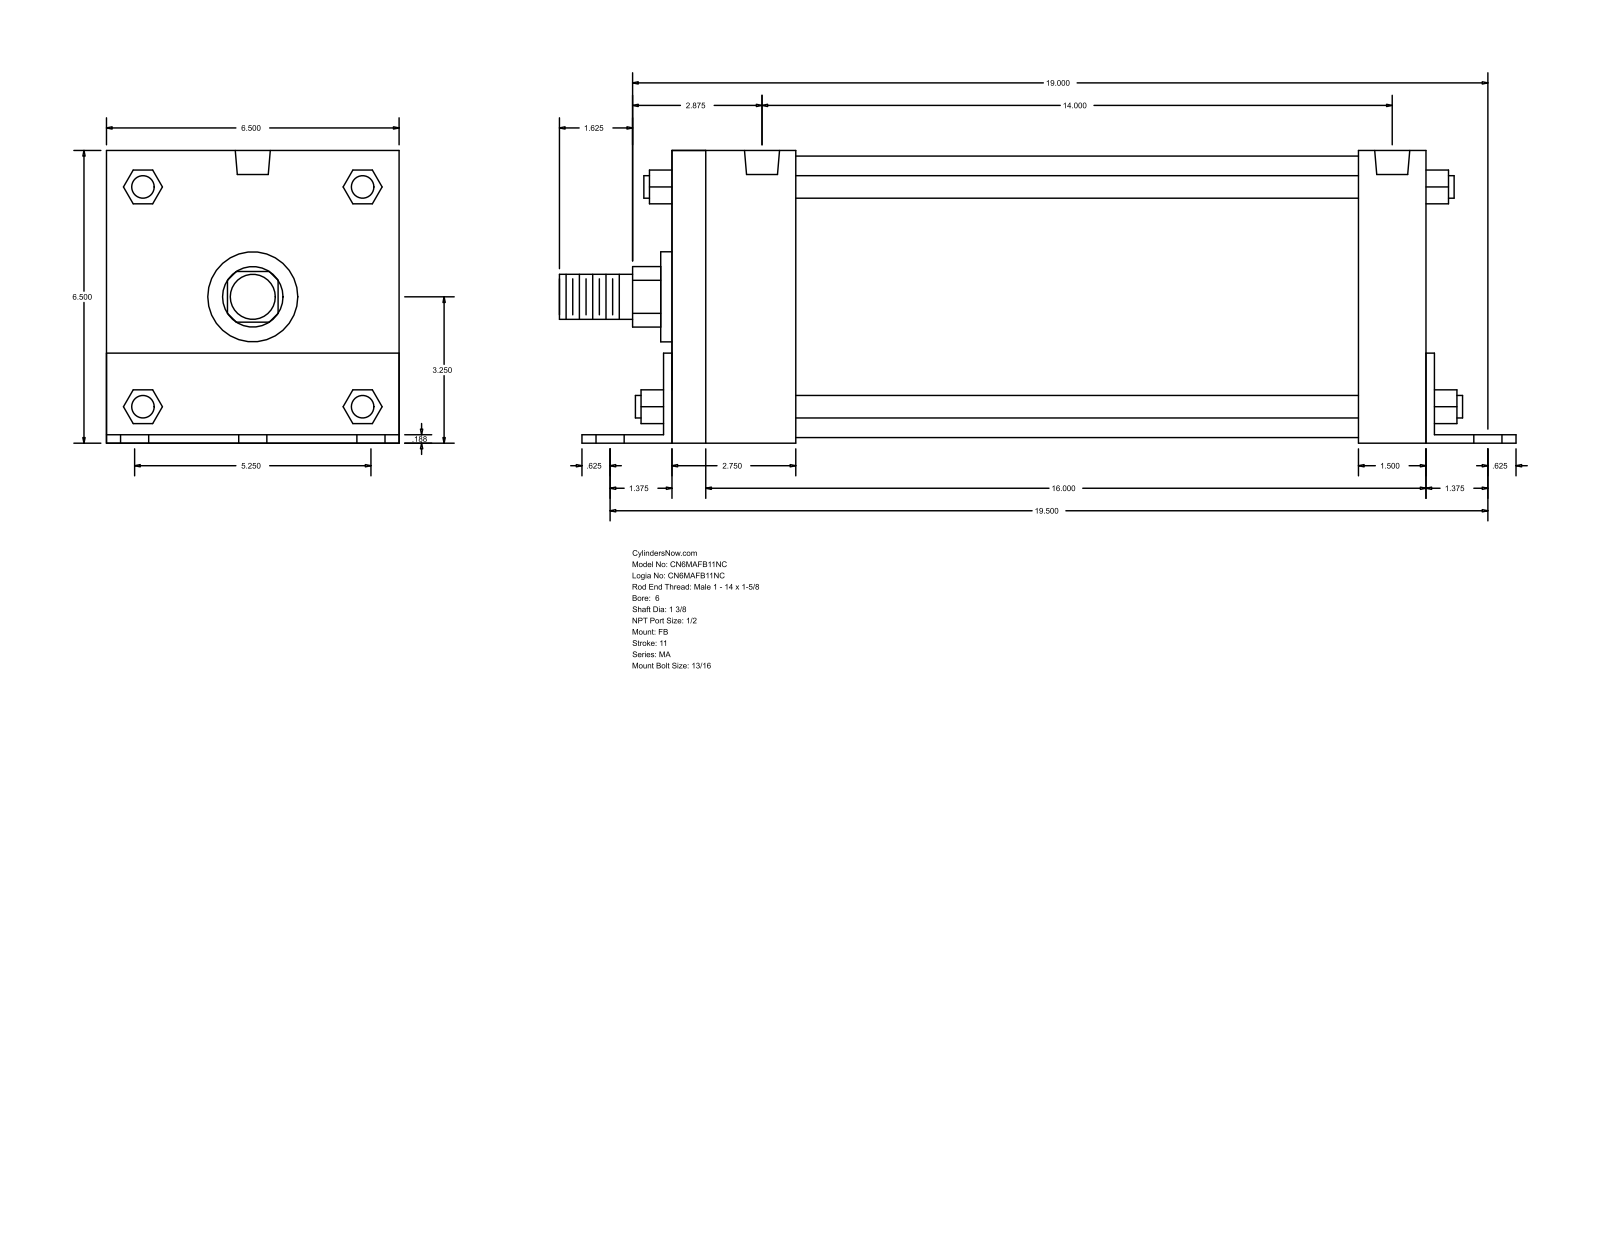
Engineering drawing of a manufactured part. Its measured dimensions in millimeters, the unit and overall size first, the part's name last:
Units: millimetres
Overall size (bounding box): 536.58 × 165.15 × 165.1
Round holes (diameter × count): ⌀20.64 ×6, ⌀17.46 ×4, ⌀19.77 ×2
Round bosses / shafts (diameter × count): ⌀12.7 ×4, ⌀158.75 ×1, ⌀50.8 ×1, ⌀34.92 ×1, ⌀25.4 ×1
Partial cylindrical surfaces — rounded edges, fillets, slot ends (radius × count): R17.06 ×1, R32.05 ×1
Main face-to-face distances: 165.1, 4.76, 422.27, 165.15, 4.71, 160.39, 4.77, 38.1, 42.86, 431.8
Hole centre spacings: 66.67, 496.63, 492.13, 83.82, 85.78, 108.6, 133.34, 352.42
Bodies: 0 solids, 140 faces (105 planar, 35 cylindrical, 0 other)
Part name (STEP PRODUCT): MA_FB__0600_1.375
STEP written by: GSSL Pune (CONFIG_CONTROL_DESIGN)
